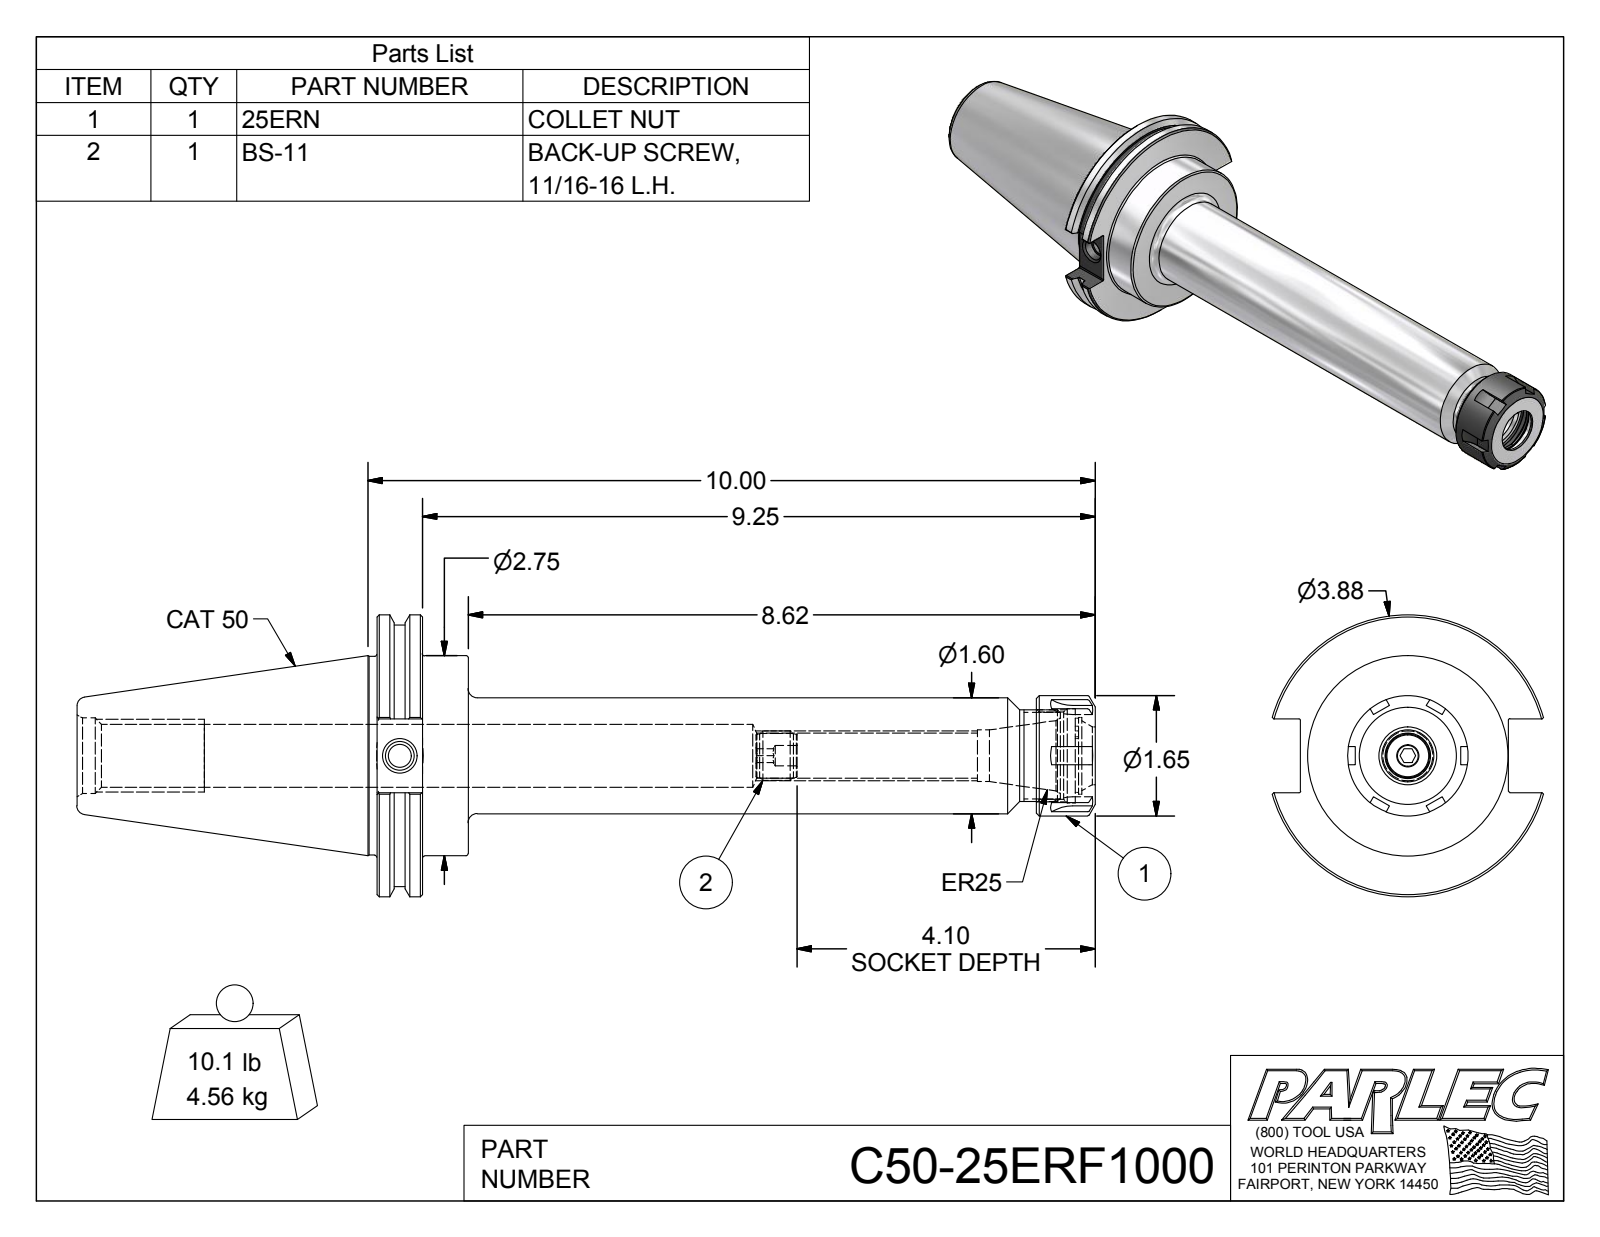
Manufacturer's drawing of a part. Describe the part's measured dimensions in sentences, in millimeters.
The part is named "C50-25ER10-1; 25ERN; BS-11; C50-25ERF1000". Its 3-D file was written by "Autodesk Inventor 2016 (AUTOMOTIVE_DESIGN)". It is 3 solids with 181 faces: 72 planar, 48 cylindrical and 61 other. Overall it measures 355.6 by 98.42 by 94.71 millimeters. Its volume is 584 473 cubic millimeters and its surface area 94 543 square millimeters. Round holes: 1 of diameter 7.11, 1 of diameter 8, 1 of diameter 10.13, 1 of diameter 15.75, 1 of diameter 18.03, 1 of diameter 20.32, 1 of diameter 21.96, 1 of diameter 21.97, 1 of diameter 26.37, 1 of diameter 30.5, 1 of diameter 32.88. Round bosses or shafts: 1 of diameter 98.42, 1 of diameter 91.29, 1 of diameter 69.85, 1 of diameter 69.34, 1 of diameter 42, 1 of diameter 40.51, 1 of diameter 32, 1 of diameter 17.3. Partial cylindrical surfaces (rounded edges, fillets, slot ends): 20 of radius 0.51, 1 of radius 12, 1 of radius 13.06, 1 of radius 13.43. The main face-to-face distances are 15.88, 31.88, 16, 250.83, 234.95, 218.95, 230.26, 214.38, 198.38, 20.57.
